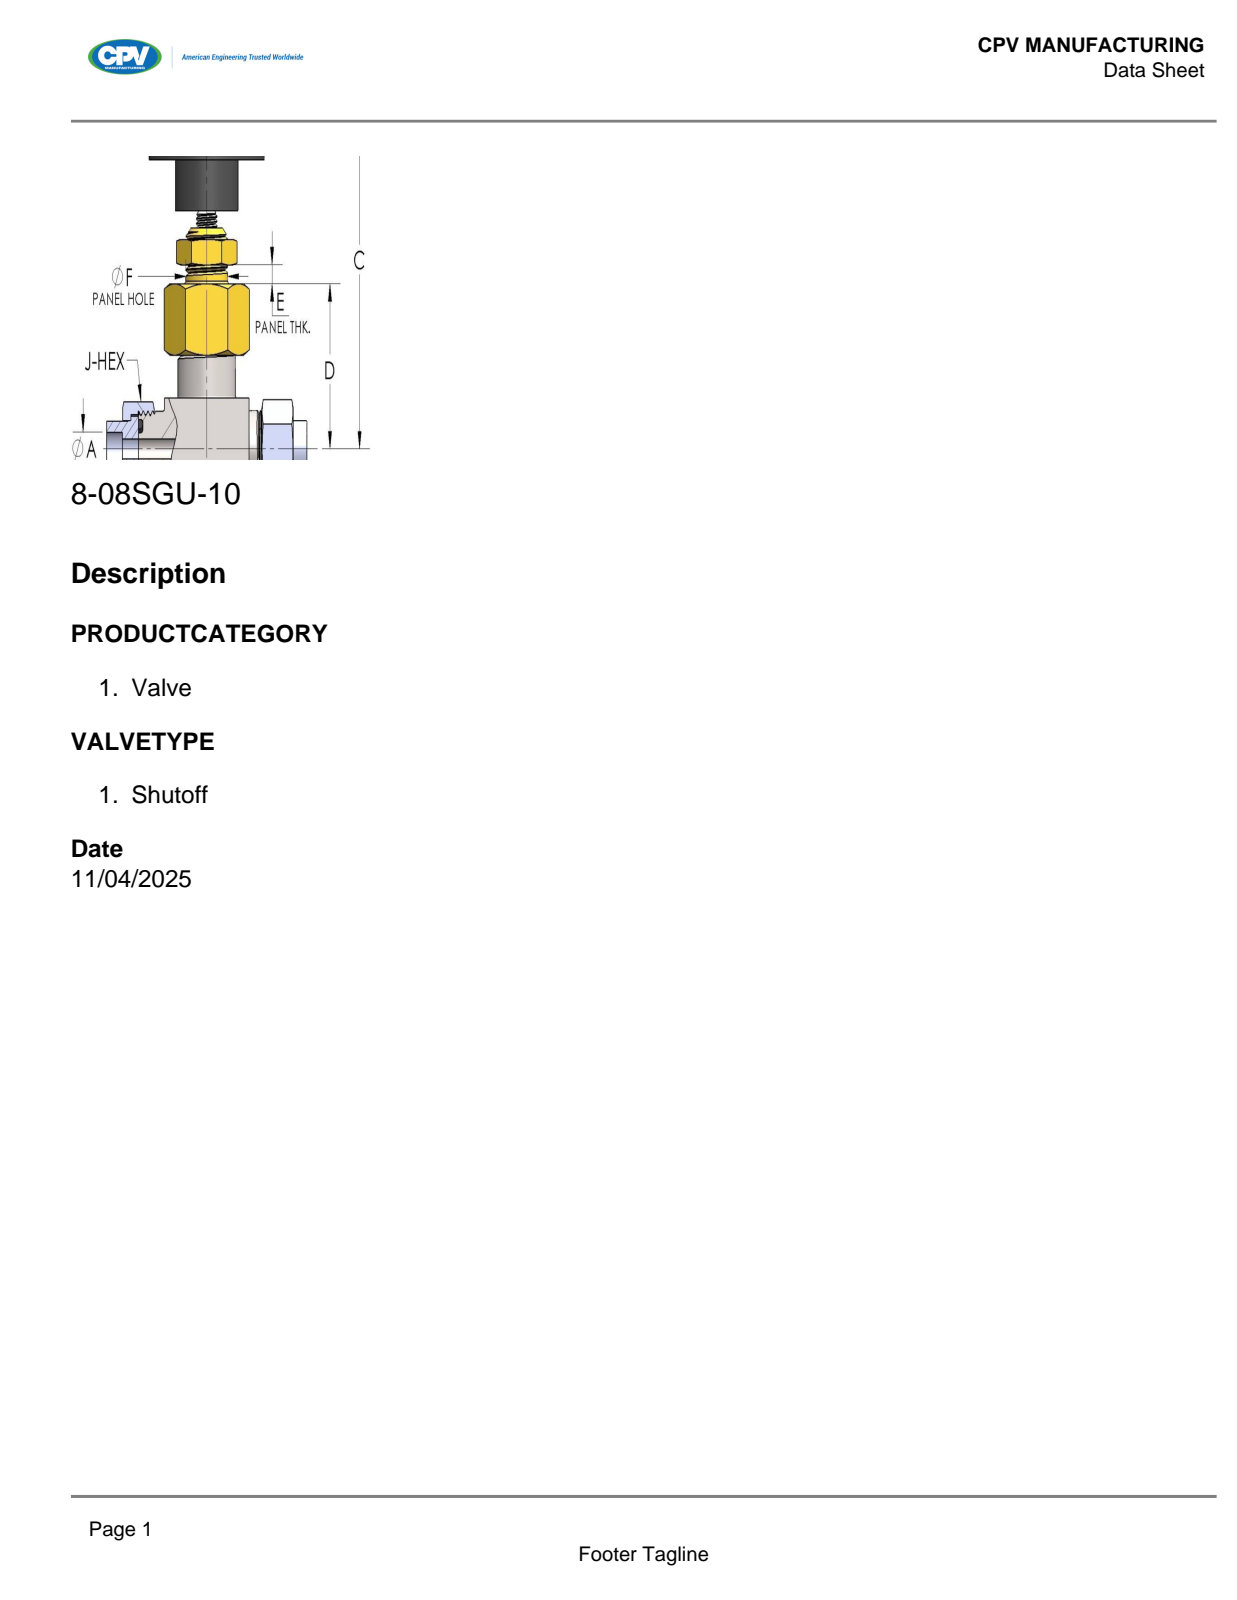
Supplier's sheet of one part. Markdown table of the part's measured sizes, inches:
| quantity | value |
| --- | --- |
| part name | 8-08SGU-10 |
| STEP written by | SolidWorks 2018 (AUTOMOTIVE_DESIGN) |
| units | inches |
| bodies | 1 solid, 169 faces (56 planar, 47 cylindrical, 66 other) |
| overall size | 3.857 × 3.64 × 1.88 |
| volume | 6.044 in³ |
| surface area | 37.14 in² |
| round holes (diameter × count) | 0.252 × 1, 0.547 × 1, 0.631 × 1 |
| round bosses / shafts (diameter × count) | 0.996 × 2, 1.88 × 1, 1 × 1, 0.815 × 1, 0.748 × 1, 0.312 × 1, 0.25 × 1 |
| main face-to-face distances | 1.128, 1.13, 1.125, 0.31, 3.457, 3.767, 1.13, 2.957, 0.5, 0.81 |
